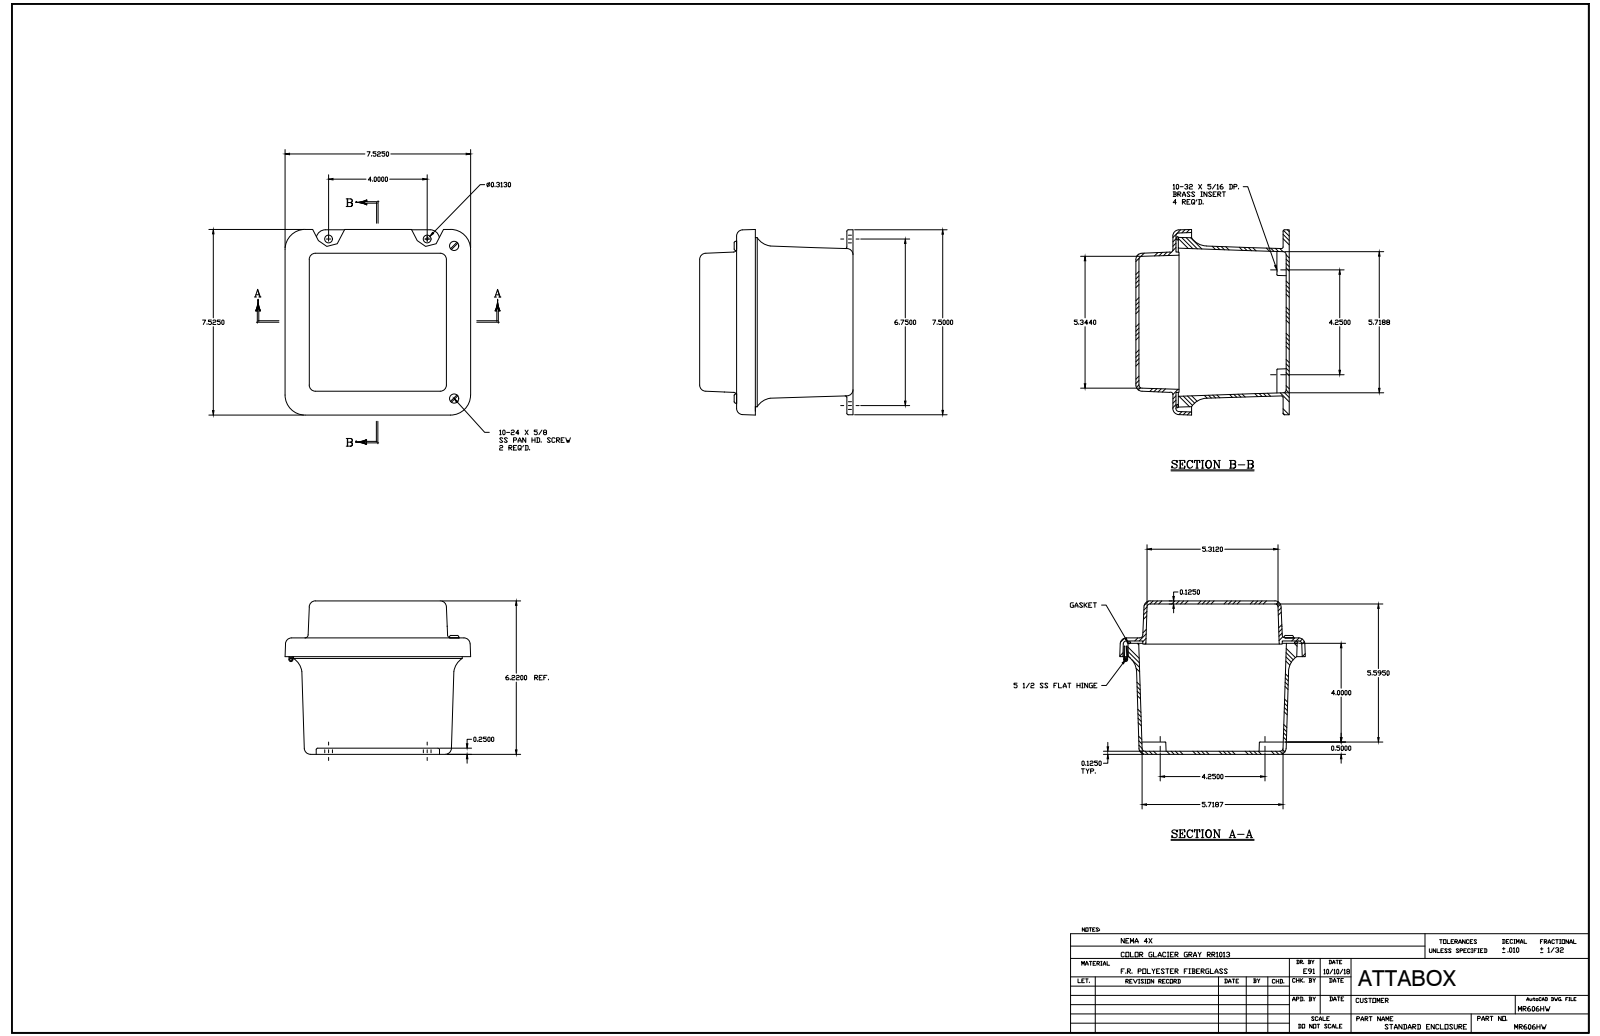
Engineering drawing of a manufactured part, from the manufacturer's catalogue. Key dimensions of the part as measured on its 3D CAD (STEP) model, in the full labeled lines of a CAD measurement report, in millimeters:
Part name (STEP PRODUCT): MR606HW
STEP written by: SolidWorks 2018 (AUTOMOTIVE_DESIGN)
Units: millimetres
Bodies: 19 solids, 716 faces (223 planar, 267 cylindrical, 226 other)
Overall size (bounding box): 191.8 × 191.1 × 161
Volume: 660 100 mm³ · Surface area: 365 200 mm²
Round holes (diameter × count): ⌀3.3 ×5, ⌀3.6 ×5, ⌀3.9 ×5, ⌀4 ×4, ⌀5.5 ×4, ⌀3.7 ×2, ⌀2.2 ×1, ⌀2.2 ×1
Round bosses / shafts (diameter × count): ⌀6.9 ×6, ⌀6.4 ×5, ⌀3.2 ×3, ⌀4.8 ×2, ⌀4 ×2, ⌀3.2 ×2, ⌀3.9 ×1, ⌀3.9 ×1
Partial cylindrical surfaces — rounded edges, fillets, slot ends (radius × count): R0.8 ×20, R3.2 ×16, R6.4 ×16, R1.6 ×4, R5.1 ×4, R7.9 ×4, R8 ×4, R9.5 ×4
Main face-to-face distances: 3.2, 3.2, 38.1, 116.5, 154.6, 157.8, 161, 157.8, 119.7, 41.3
Hole centre spacings: 134.8, 34.8, 63.5, 108, 157.1, 187.5, 12.7, 50.8
